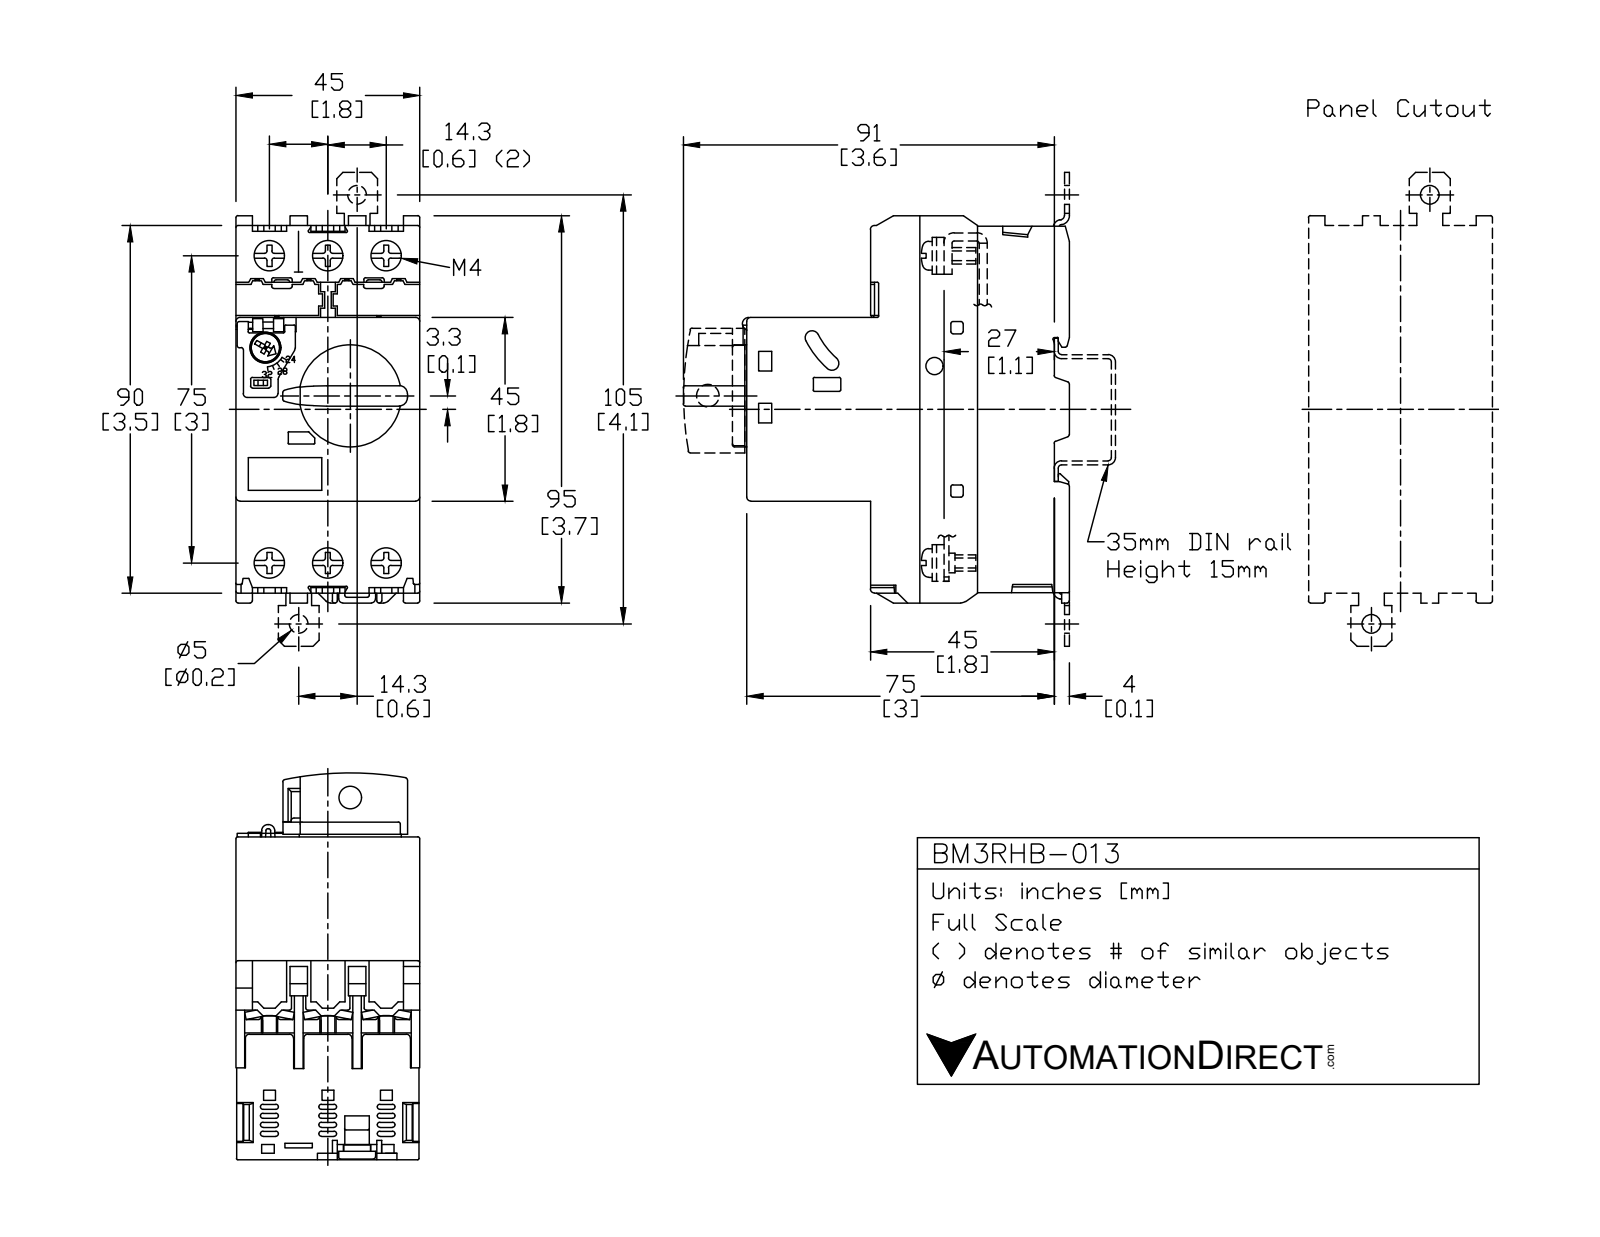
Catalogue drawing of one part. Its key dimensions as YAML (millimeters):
part_name: "BM3RHB-013"
step_written_by: "SolidWorks 2018 (AUTOMOTIVE_DESIGN)"
units: millimeters
bodies: {solids: 25, faces: 1294, planar: 964, cylindrical: 327, other: 3}
overall_size: [94.8, 94.5, 45]
volume: 231500
surface_area: 57040
round_holes:
  - {diameter: 4, count: 6}
  - {diameter: 7.4, count: 6}
  - {diameter: 1.6, count: 1}
  - {diameter: 4.2, count: 1}
  - {diameter: 5, count: 1}
  - {diameter: 5.5, count: 1}
  - {diameter: 7.5, count: 1}
round_bosses_or_shafts:
  - {diameter: 6, count: 6}
  - {diameter: 25, count: 1}
  - {diameter: 7, count: 1}
partial_cylinders:
  - {radius: 0.5, count: 67}
  - {radius: 0.6, count: 24}
  - {radius: 2, count: 14}
  - {radius: 0.3, count: 12}
  - {radius: 1, count: 8}
  - {radius: 2.5, count: 8}
  - {radius: 0.2, count: 6}
  - {radius: 1.5, count: 2}
face_to_face_distances: [45, 36.6, 42.4, 79, 22.4, 67.4, 3, 16.5, 20.1, 12]
hole_center_spacings: [14.3, 76.4, 75, 28.6, 80.3, 22.4, 23.9, 27.1]
